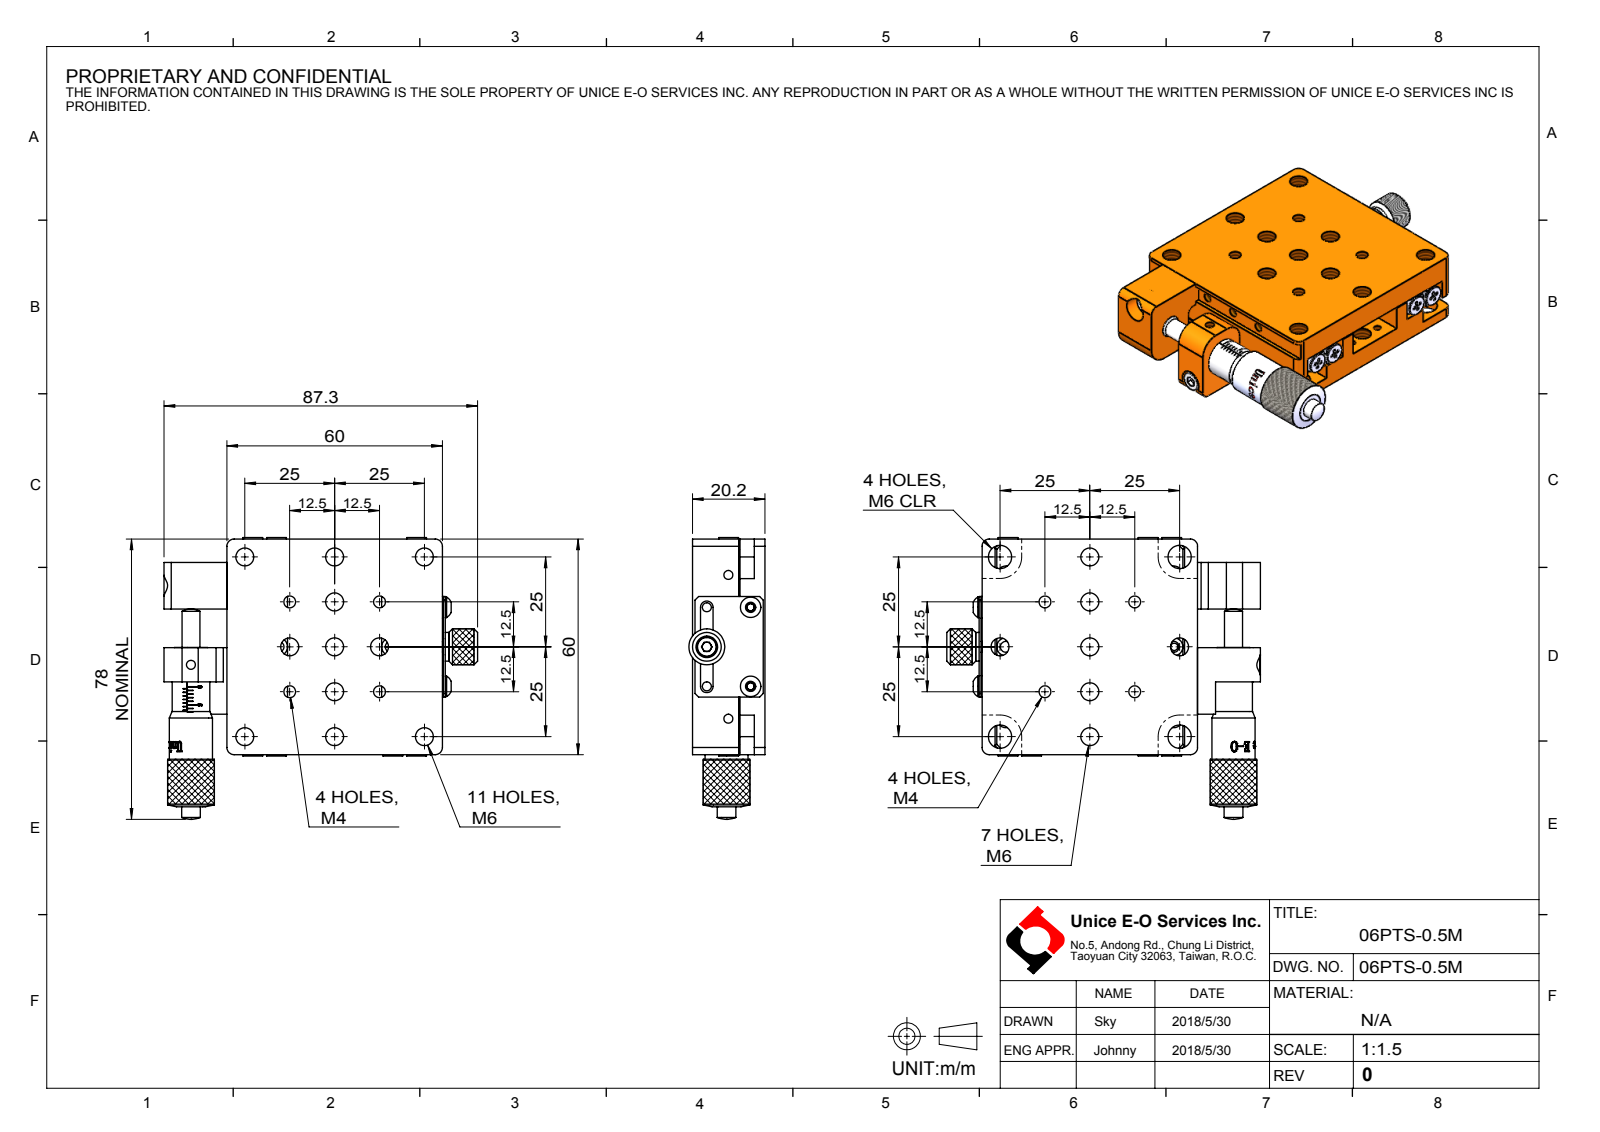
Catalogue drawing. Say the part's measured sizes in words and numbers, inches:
The part is named "06PTS-0.5M". Its 3-D file was written by "SolidWorks 2016 (AUTOMOTIVE_DESIGN)". It is 0 solids with 666 faces: 371 planar, 192 cylindrical and 103 other. Overall it measures 3.437 by 3.087 by 0.835 inches. Round holes: 15 of diameter 0.197, 10 of diameter 0.098, 7 of diameter 0.256, 4 of diameter 0.081, 4 of diameter 0.13, 1 of diameter 0.118, 1 of diameter 0.236, 1 of diameter 0.374, 1 of diameter 0.417. Round bosses or shafts: 6 of diameter 0.217, 3 of diameter 0.236, 2 of diameter 0.224, 1 of diameter 0.512, 1 of diameter 0.472, 1 of diameter 0.413, 1 of diameter 0.394, 1 of diameter 0.315. Partial cylindrical surfaces (rounded edges, fillets, slot ends): 7 of radius 0.079, 4 of radius 0.197, 4 of radius 0.236, 2 of radius 0.069, 1 of radius 0.235. The main face-to-face distances are 0.795, 0.52, 0.276, 0.28, 0.24, 0.516, 0.236, 0.043, 0.039, 2.362. The hole center spacings are 1.1, 0.696, 0.984, 0.492, 1.556, 1.392, 0.394, 1.774.
